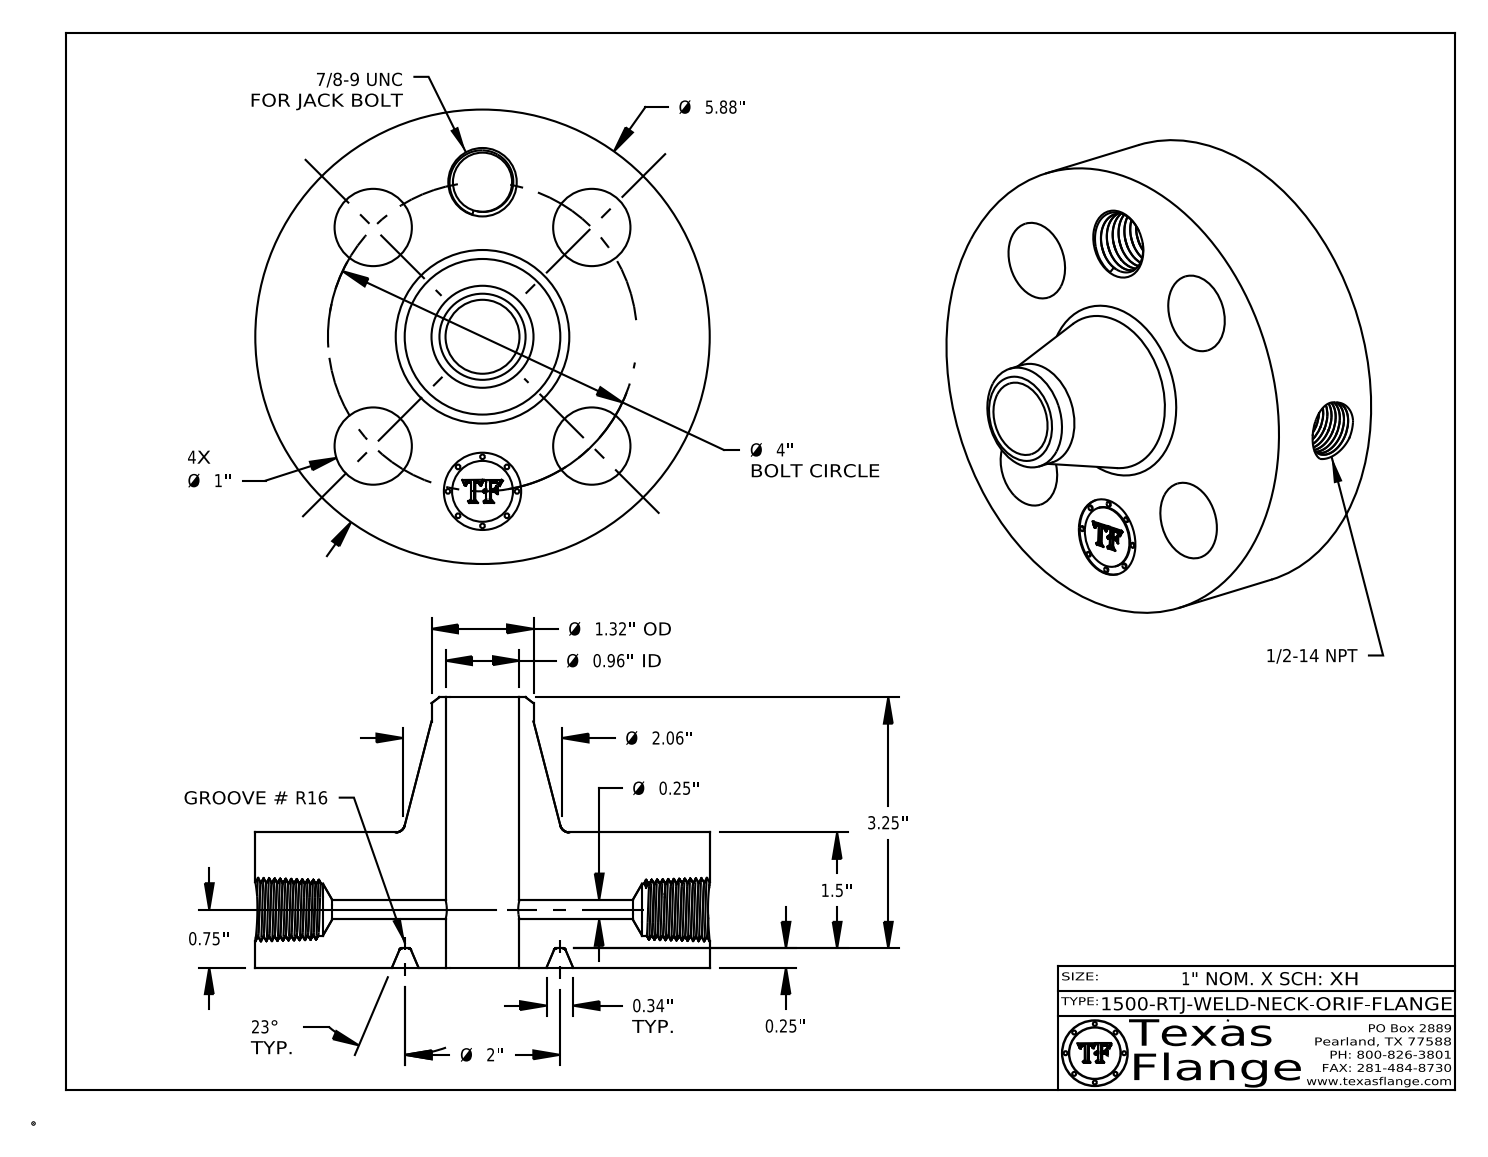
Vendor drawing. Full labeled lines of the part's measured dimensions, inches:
Part name (STEP PRODUCT): 1500-RTJ-WELD-NECK
STEP written by: CATIA V5 STEP AP214 (AUTOMOTIVE_DESIGN)
Units: inches
Bodies: 1 solid, 771 faces (370 planar, 85 cylindrical, 316 other)
Overall size (bounding box): 5.88 × 5.88 × 3.5
Volume: 40.97 in³ · Surface area: 134.8 in²
Round holes (diameter × count): ⌀1 ×5, ⌀0.25 ×1, ⌀0.672 ×1, ⌀0.766 ×1, ⌀0.957 ×1
Round bosses / shafts (diameter × count): ⌀0.061 ×8, ⌀5.88 ×1, ⌀1.32 ×1, ⌀0.788 ×1
Main face-to-face distances: 1.75, 0.25, 1.5, 1.735, 1.485, 0.015, 3.5, 3.25, 1.765, 0.298
Hole centre spacings: 2, 1.531, 2.828, 3.695, 4
